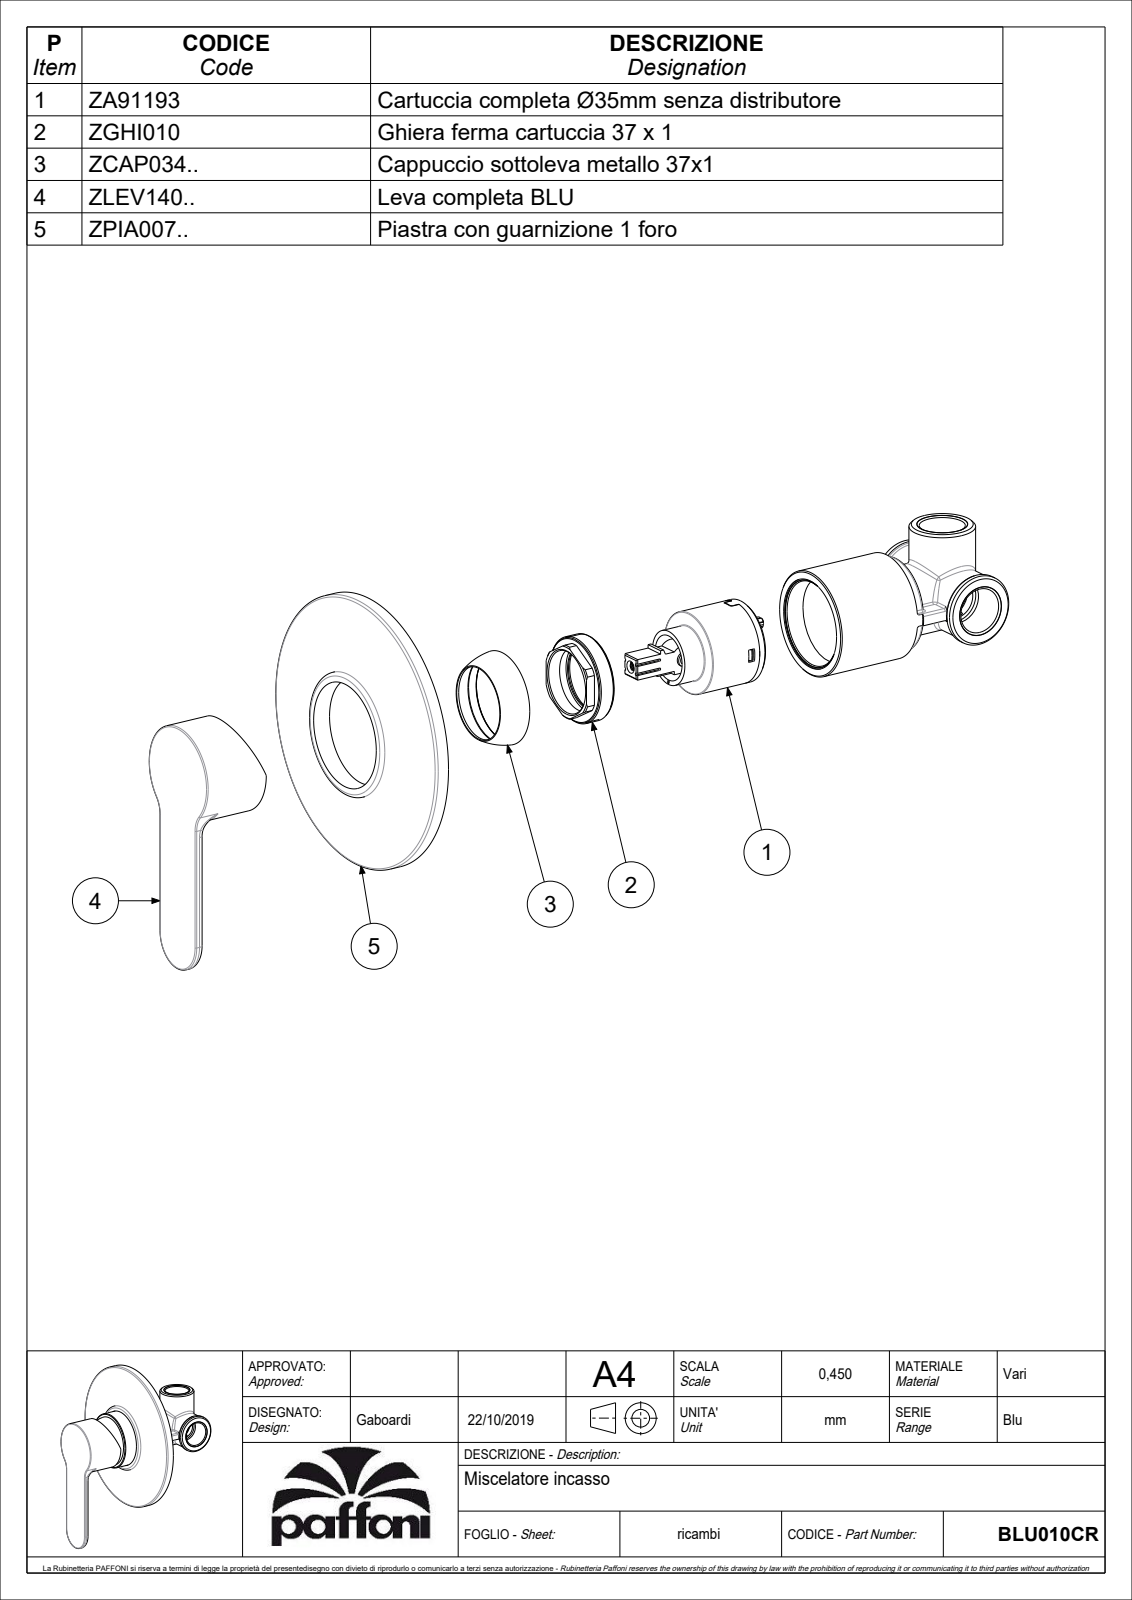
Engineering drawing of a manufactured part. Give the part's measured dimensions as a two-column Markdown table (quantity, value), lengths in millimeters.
| quantity | value |
| --- | --- |
| part name | BLU010CR |
| STEP written by | CREO PARAMETRIC BY PTC INC, 2020044 (CONFIG_CONTROL_DESIGN) |
| units | millimeters |
| bodies | 2 solids, 728 faces (340 planar, 233 cylindrical, 155 other) |
| overall size | 143 × 116 × 64.8 |
| volume | 66 701 mm³ |
| surface area | 65 945 mm² |
| round holes (diameter × count) | 8 × 3, 12 × 3, 2 × 2, 7 × 2, 3 × 1, 3.3 × 1, 3.4 × 1, 4 × 1, 4.5 × 1, 4.6 × 1, 9.5 × 1, 19.5 × 1 |
| round bosses / shafts (diameter × count) | 4.8 × 2, 116 × 1, 53 × 1, 44.8 × 1, 42 × 1, 35 × 1, 34.8 × 1, 32.2 × 1 |
| partial cylindrical surfaces (radius × count) | 0.5 × 41, 0.3 × 19, 1.2 × 10, 1 × 9, 4.5 × 3, 1.6 × 2, 2.5 × 2, 10 × 2 |
| main face-to-face distances | 60.3, 1, 23, 61.3, 26.2, 0.5, 5.3, 9, 3.45, 1.5 |
| hole center spacings | 0.71, 8.51, 8.6, 9.85, 10.42, 12, 12.14, 13.04 |
